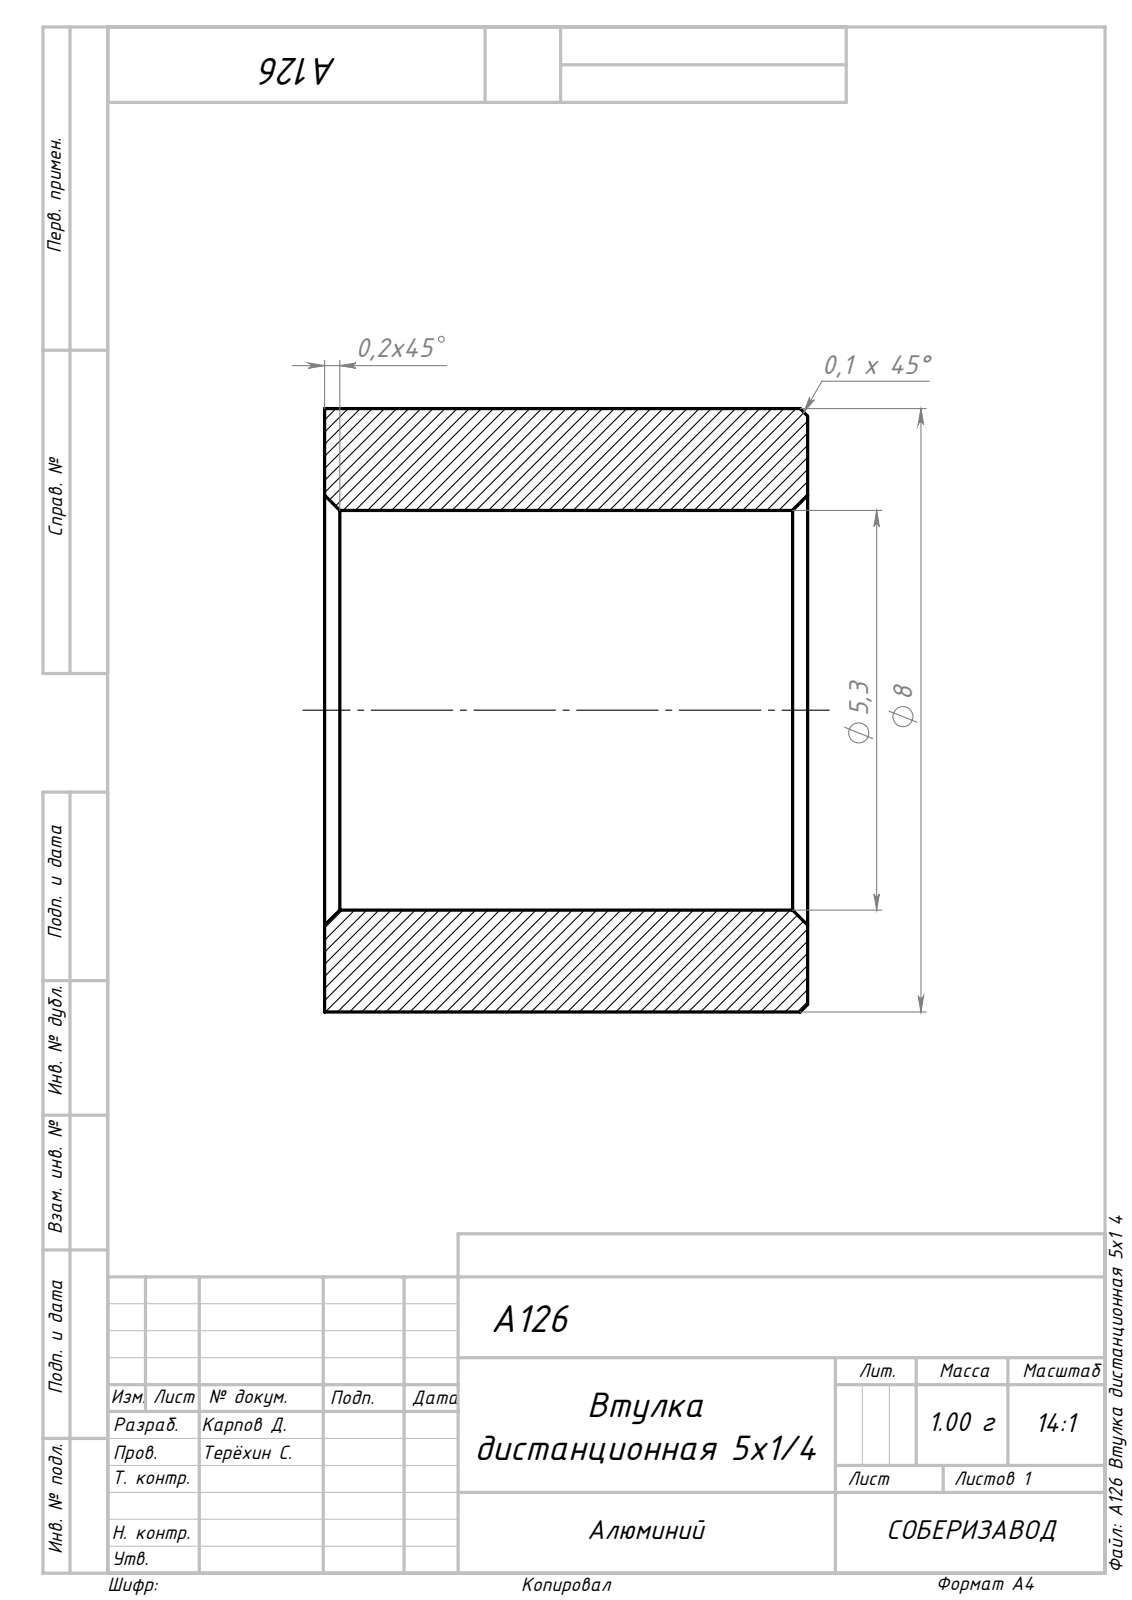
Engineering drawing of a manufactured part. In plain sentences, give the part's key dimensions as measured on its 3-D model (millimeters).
The part is named "A126 Втулка дистанционная 5х1 4". Its 3-D file was written by "SolidWorks 2020 (AUTOMOTIVE_DESIGN)". It is 1 solid with 12 faces: 2 planar, 4 cylindrical and 6 other. Overall it measures 8 by 8 by 6.4 millimeters. Its volume is 180 cubic millimeters and its surface area 319 square millimeters. Round holes: 1 of diameter 5.3. Round bosses or shafts: 1 of diameter 8. The main face-to-face distances are 6.4.
